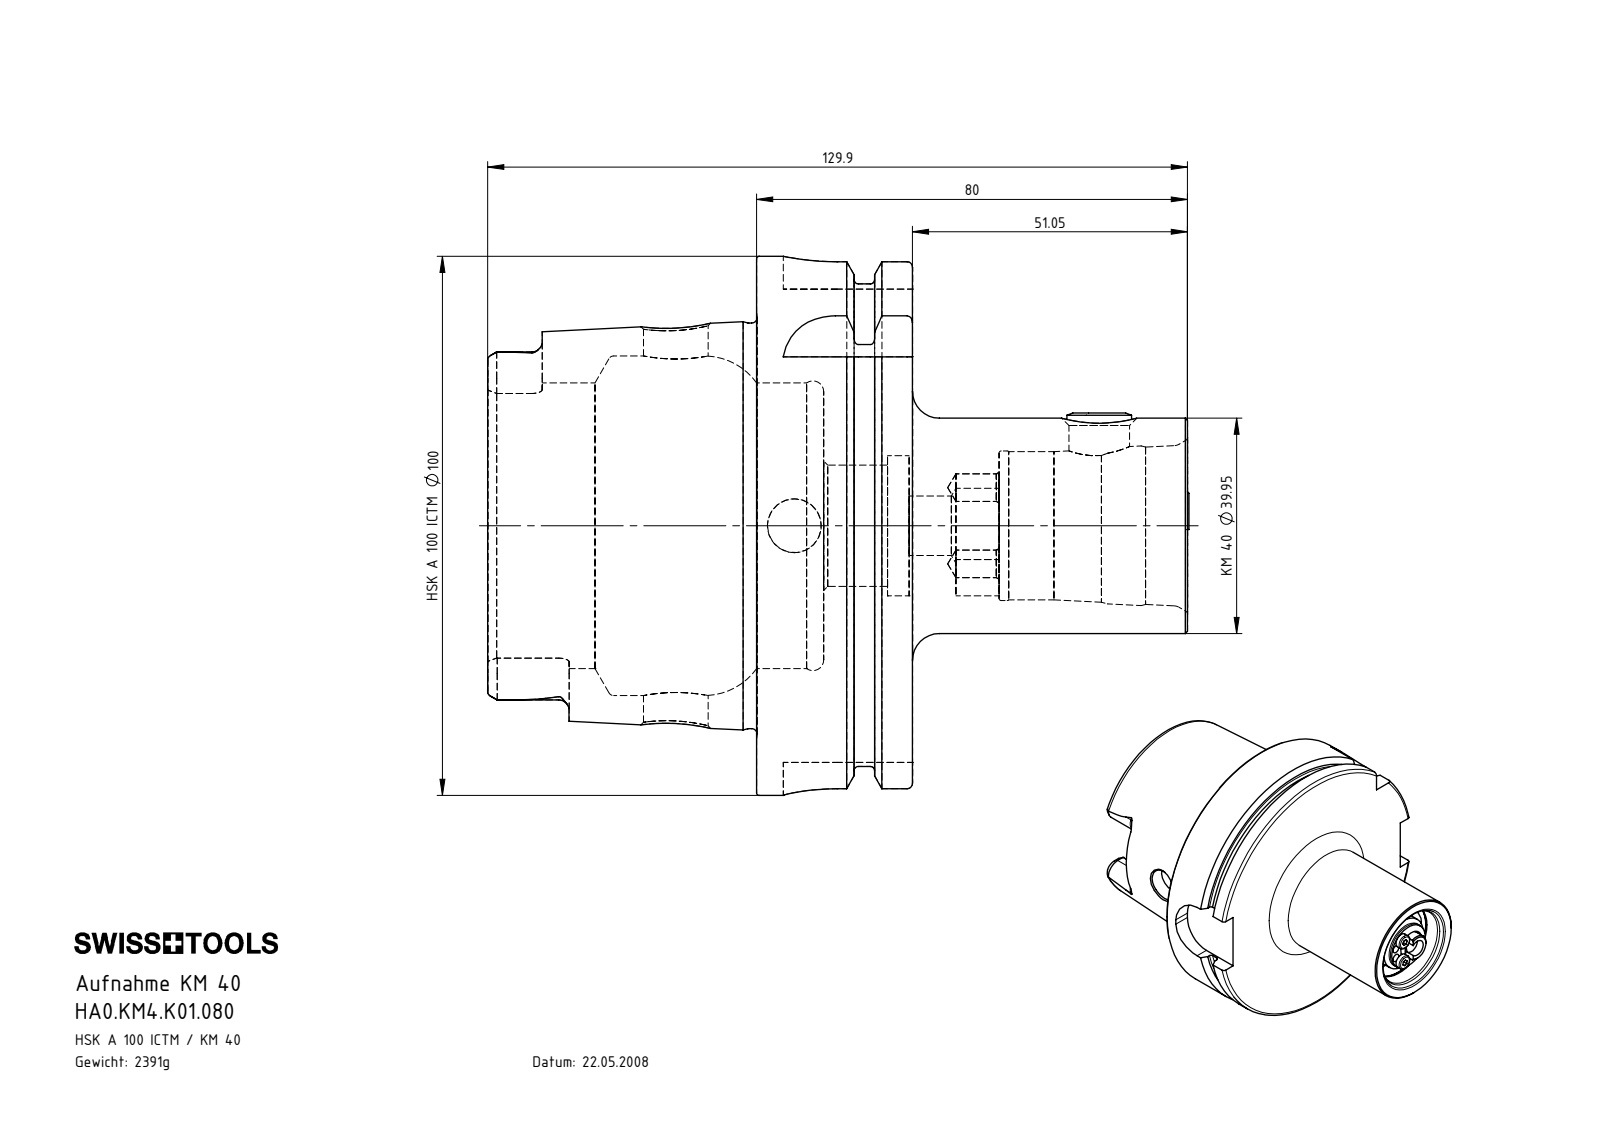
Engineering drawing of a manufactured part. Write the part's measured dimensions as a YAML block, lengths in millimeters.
part_name: "KM4-ER1.005.016_A; KM4-ER1.006.014_A; HA0-KM4.K01.080_C_Fertigbearbeitung; DIN 3771 - 9.25x1.78 (+8 more)"
step_written_by: "SolidWorks 2017 (AUTOMOTIVE_DESIGN)"
units: millimeters
bodies: {solids: 14, faces: 619, planar: 159, cylindrical: 199, other: 261}
overall_size: [130.16, 100, 100]
volume: 305483
surface_area: 70561
round_holes:
  - {diameter: 5, count: 6}
  - {diameter: 3, count: 4}
  - {diameter: 5.11, count: 4}
  - {diameter: 2.5, count: 2}
  - {diameter: 3.2, count: 2}
  - {diameter: 3.5, count: 1}
  - {diameter: 6, count: 1}
  - {diameter: 7, count: 1}
  - {diameter: 9.09, count: 1}
  - {diameter: 10, count: 1}
  - {diameter: 10.02, count: 1}
  - {diameter: 11, count: 1}
round_bosses_or_shafts:
  - {diameter: 12, count: 2}
  - {diameter: 5.5, count: 2}
  - {diameter: 3, count: 2}
  - {diameter: 100, count: 1}
  - {diameter: 91.95, count: 1}
  - {diameter: 75.26, count: 1}
  - {diameter: 39.95, count: 1}
  - {diameter: 27.43, count: 1}
partial_cylinders:
  - {radius: 0.2, count: 10}
  - {radius: 1.9, count: 6}
  - {radius: 4.88, count: 4}
  - {radius: 10, count: 4}
  - {radius: 0.4, count: 2}
  - {radius: 1.5, count: 2}
  - {radius: 3.17, count: 2}
  - {radius: 4, count: 2}
face_to_face_distances: [28.95, 12.45, 16.5, 49.9, 62.35, 78.85, 94.9, 45, 32.55, 16.05]
hole_center_spacings: [10, 14.14, 4.1, 5.97, 7.02, 7.36, 7.49, 9]
